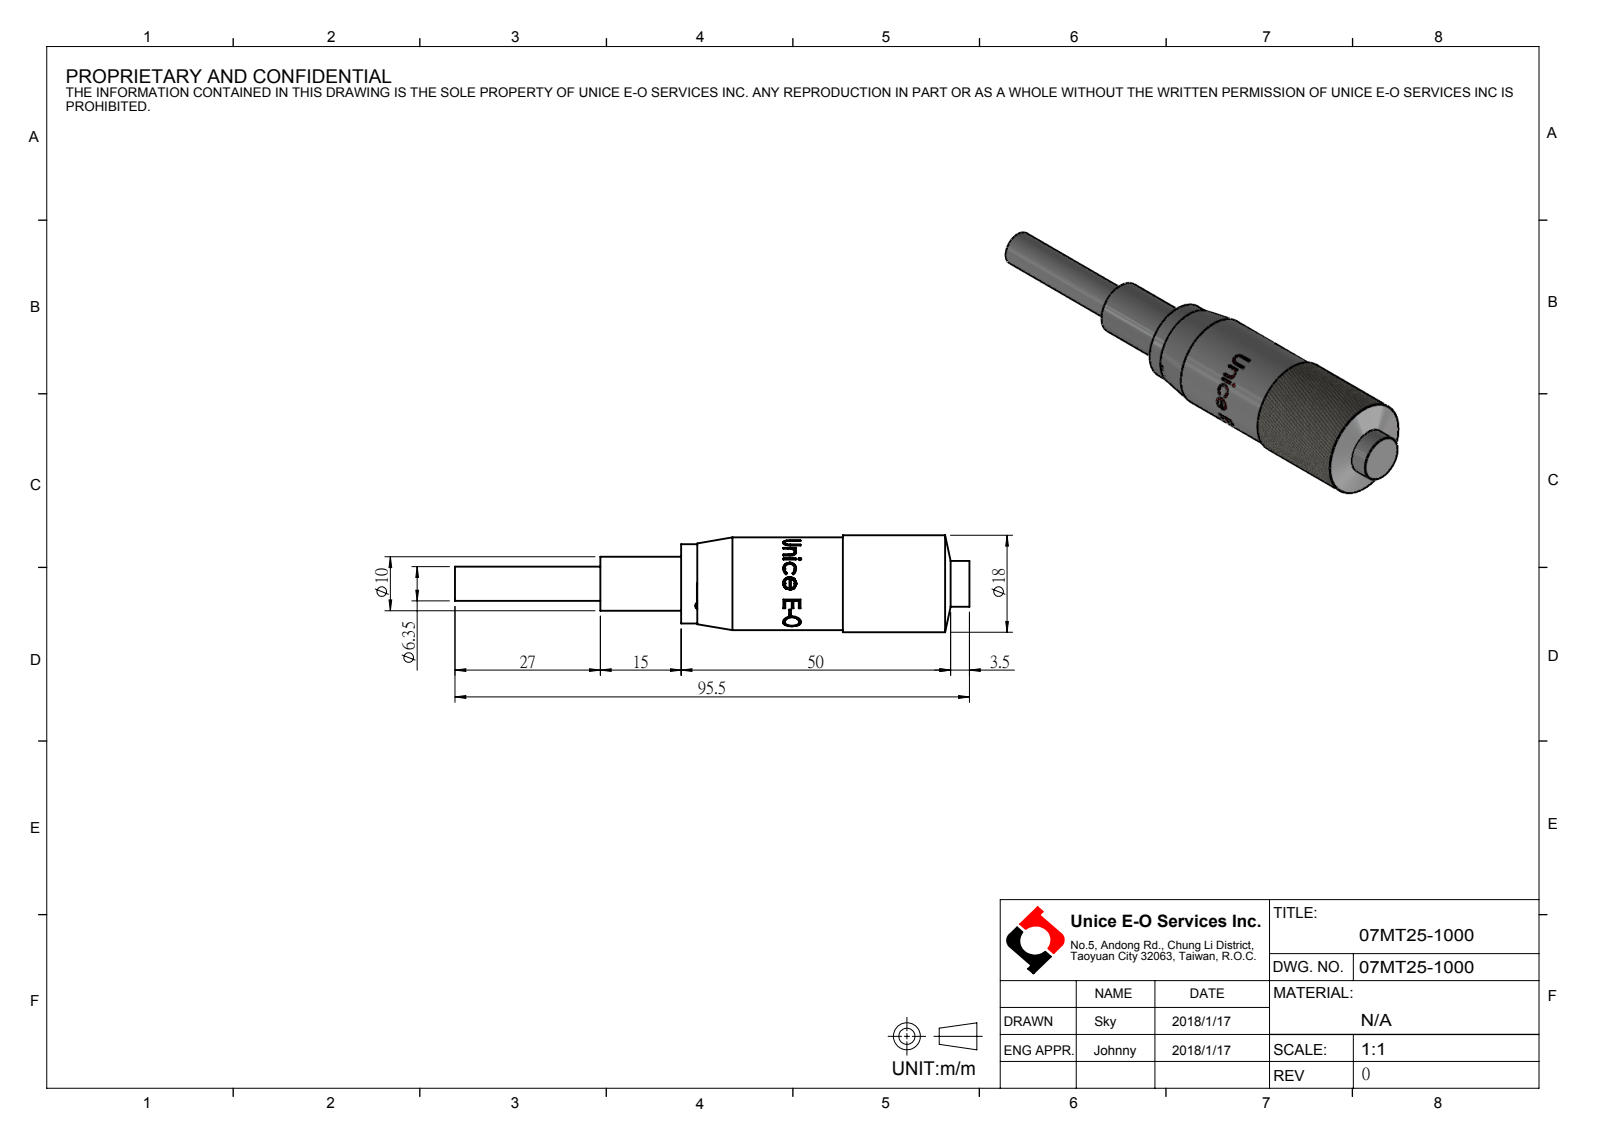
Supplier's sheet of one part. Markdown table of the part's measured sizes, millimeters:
| quantity | value |
| --- | --- |
| part name | 07MT25-1000 |
| STEP written by | SolidWorks 2016 (AUTOMOTIVE_DESIGN) |
| units | millimeters |
| bodies | 0 solids, 74 faces (18 planar, 25 cylindrical, 31 other) |
| overall size | 95.5 × 18 × 18 |
| round bosses / shafts (diameter × count) | 18 × 1, 17.2 × 1, 14.7 × 1, 10 × 1, 8.5 × 1, 6.35 × 1 |
| partial cylindrical surfaces (radius × count) | 8.55 × 1 |
| main face-to-face distances | 53.5, 15, 68.5, 27, 42, 95.5, 45, 72, 30, 23.5 |
